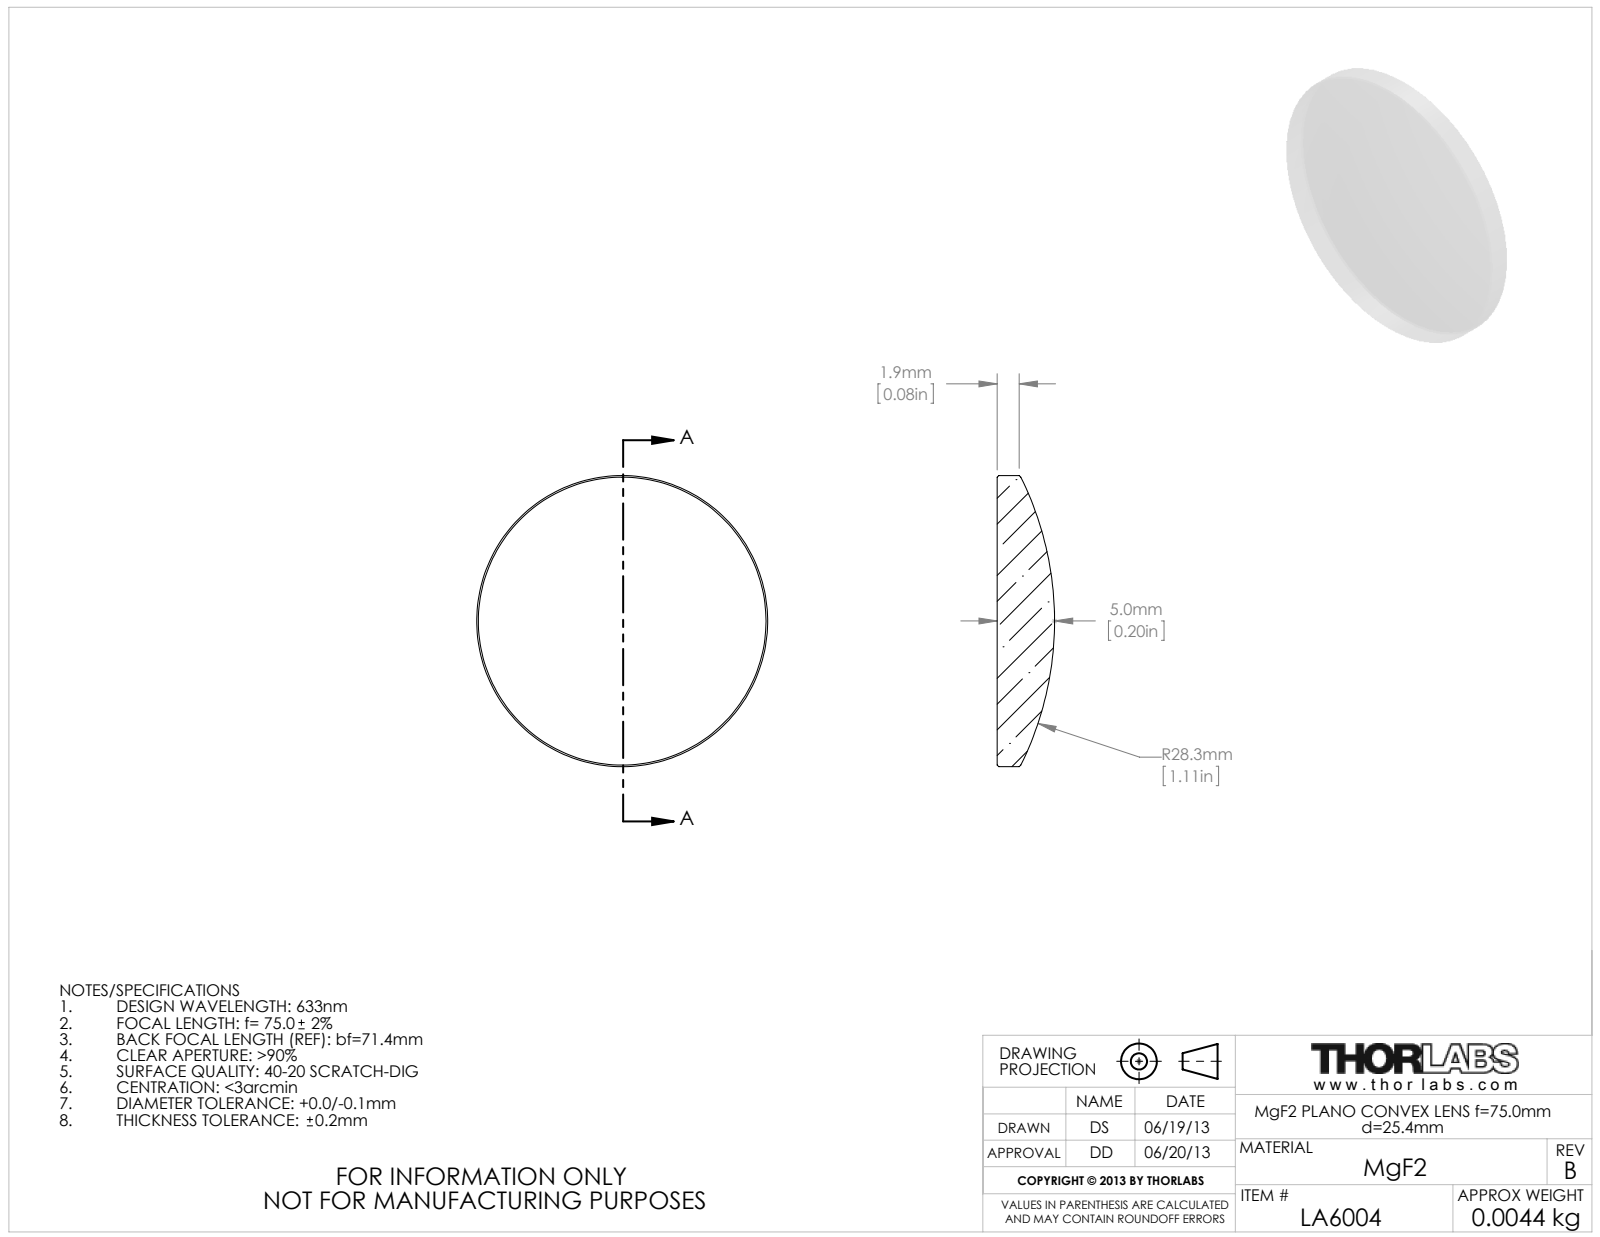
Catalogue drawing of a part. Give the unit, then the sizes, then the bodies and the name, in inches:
Units: inches
Overall size (bounding box): 1 × 1 × 0.197
Round bosses / shafts (diameter × count): ⌀1 ×1
Bodies: 0 solids, 5 faces (1 planar, 2 cylindrical, 2 other)
Part name (STEP PRODUCT): 7255-E0W
STEP written by: SolidWorks 2007 (AUTOMOTIVE_DESIGN)
